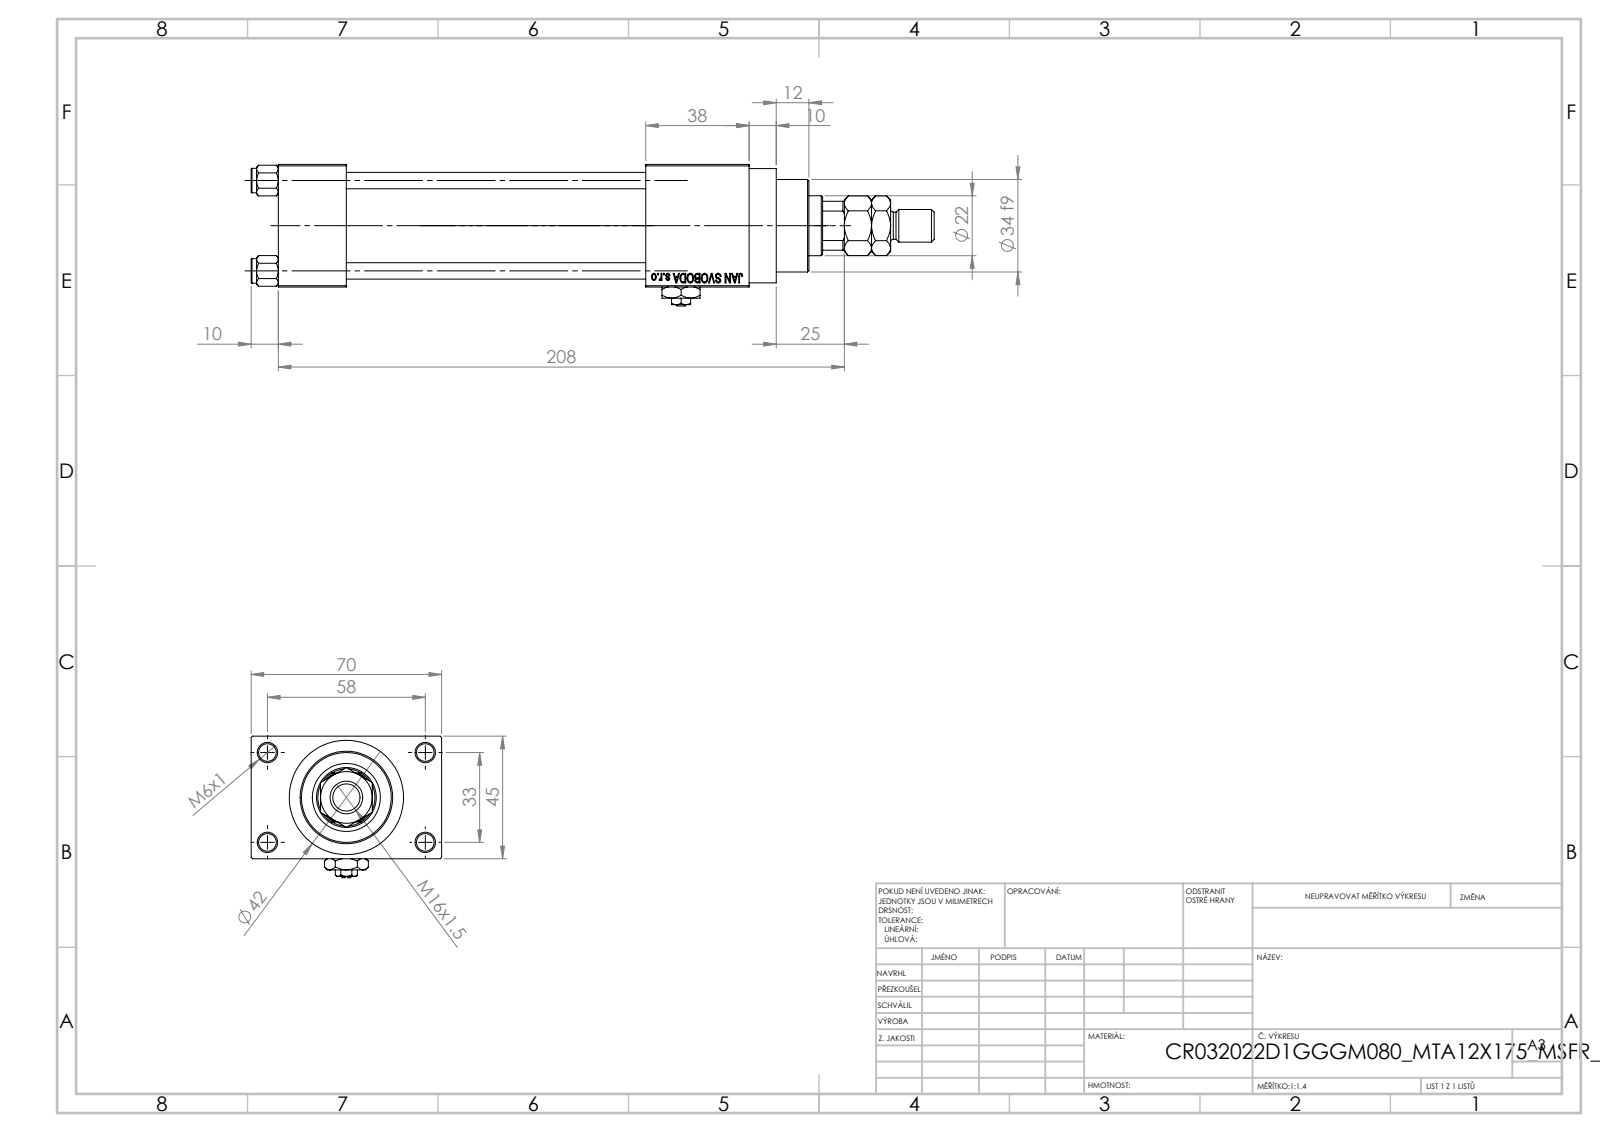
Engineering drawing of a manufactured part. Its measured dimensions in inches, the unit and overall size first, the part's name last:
Units: inches
Overall size (bounding box): 9.882 × 2.756 × 2.047
Round holes (diameter × count): ⌀0.236 ×4, ⌀0.256 ×4, ⌀0.276 ×2, ⌀0.518 ×2, ⌀0.787 ×2, ⌀0.413 ×1, ⌀0.866 ×1, ⌀0.945 ×1, ⌀0.984 ×1, ⌀1.26 ×1, ⌀1.299 ×1
Round bosses / shafts (diameter × count): ⌀0.354 ×4, ⌀1.654 ×1, ⌀1.496 ×1, ⌀1.339 ×1, ⌀0.472 ×1, ⌀0.394 ×1
Partial cylindrical surfaces — rounded edges, fillets, slot ends (radius × count): R0.413 ×1
Main face-to-face distances: 1.772, 0.984, 0.492, 2.264, 4.331, 5.315, 5.827, 2.756, 1.496, 6.811
Hole centre spacings: 0.488, 0.924, 1.307, 1.314, 1.392, 1.795, 2.219, 1.299
Volume: 18.36 in³ · Surface area: 161.6 in²
Bodies: 13 solids, 1199 faces (534 planar, 97 cylindrical, 568 other)
Part name (STEP PRODUCT): Zatka_pro_OIL_PORT; NUT_M5_D; V215_VC_A; MTA (+3 more)
STEP written by: SolidWorks 2019 (CONFIG_CONTROL_DESIGN)
